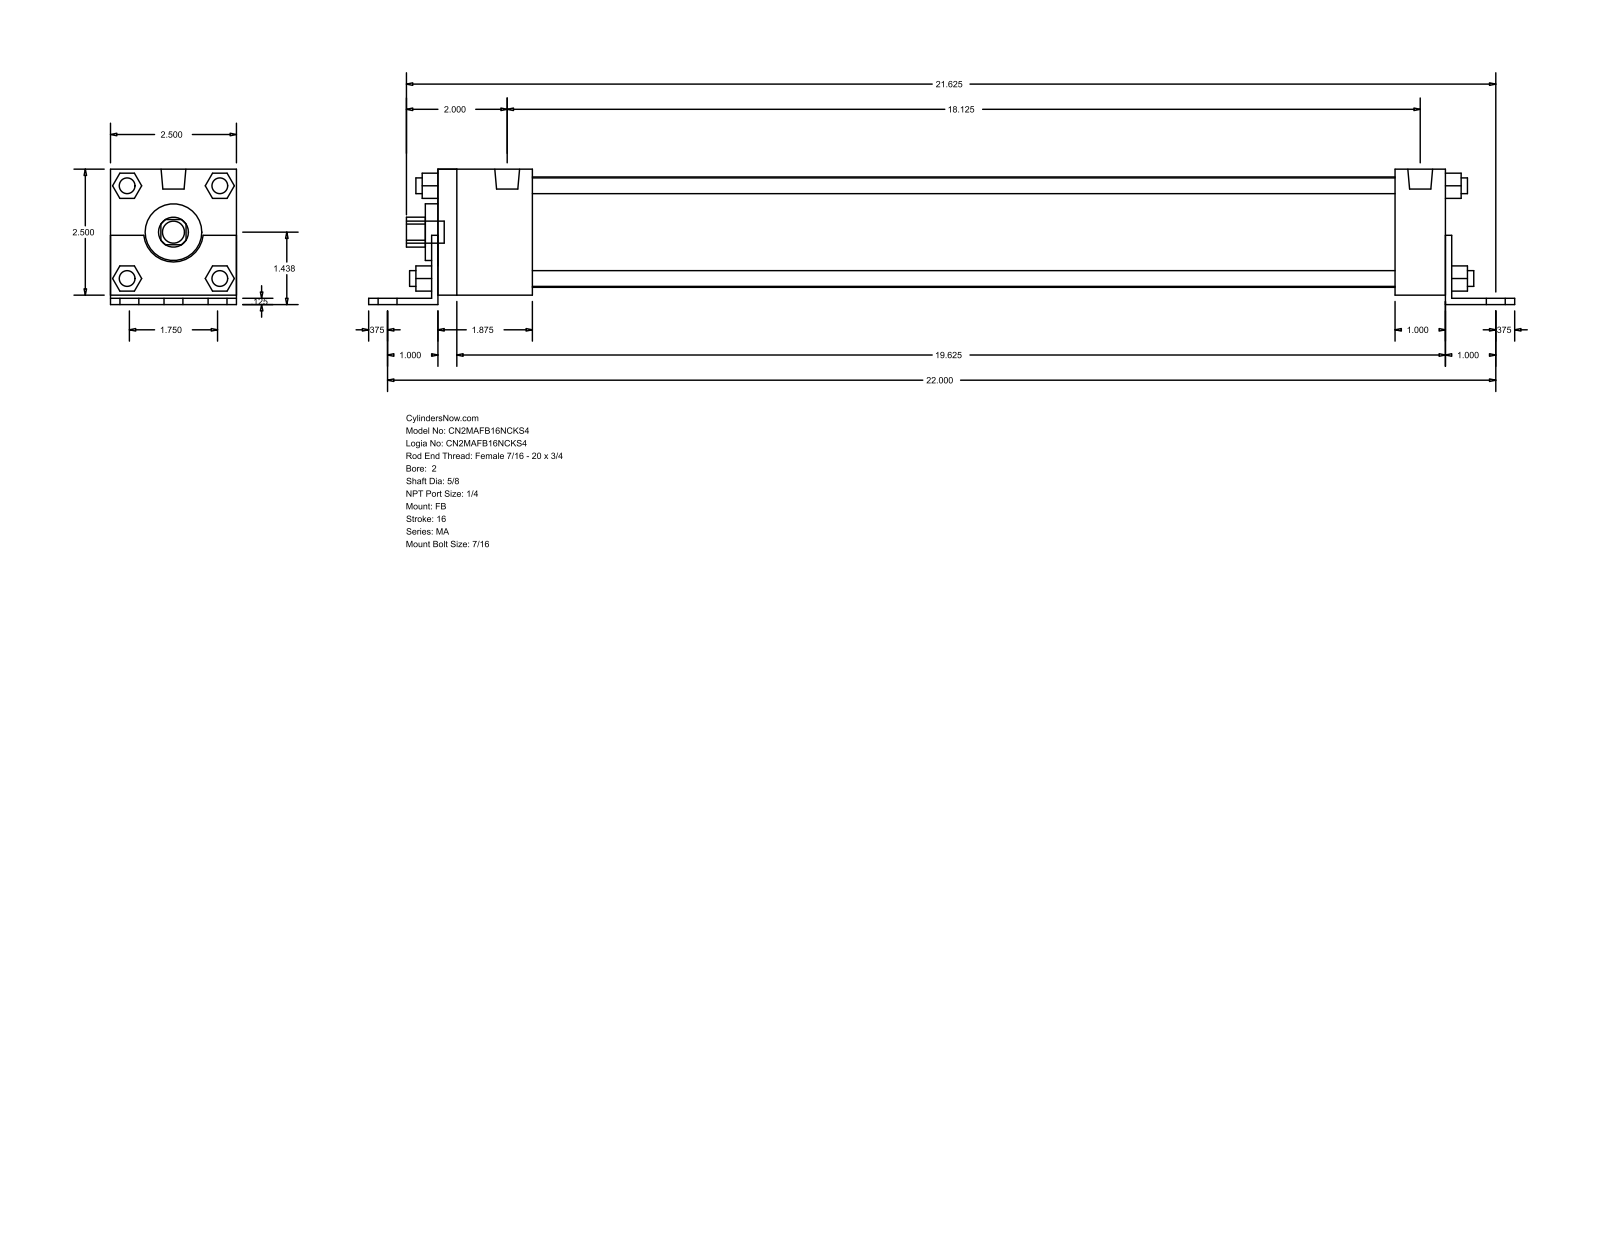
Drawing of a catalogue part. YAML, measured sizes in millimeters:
part_name: "MA_FB__0200_0.625"
step_written_by: "GSSL Pune (CONFIG_CONTROL_DESIGN)"
units: millimeters
bodies: {solids: 0, faces: 140, planar: 105, cylindrical: 35, other: 0}
overall_size: [577.85, 68.26, 63.5]
round_holes:
  - {diameter: 15.88, count: 1}
  - {diameter: 28.57, count: 1}
  - {diameter: 55.63, count: 1}
round_bosses_or_shafts:
  - {diameter: 7.94, count: 8}
  - {diameter: 11.11, count: 7}
  - {diameter: 12.49, count: 2}
partial_cylinders:
  - {radius: 7.54, count: 1}
  - {radius: 15.05, count: 1}
face_to_face_distances: [63.5, 3.17, 4.76, 68.26, 1.59, 65.09, 508, 514.35, 3.18, 511.17]
